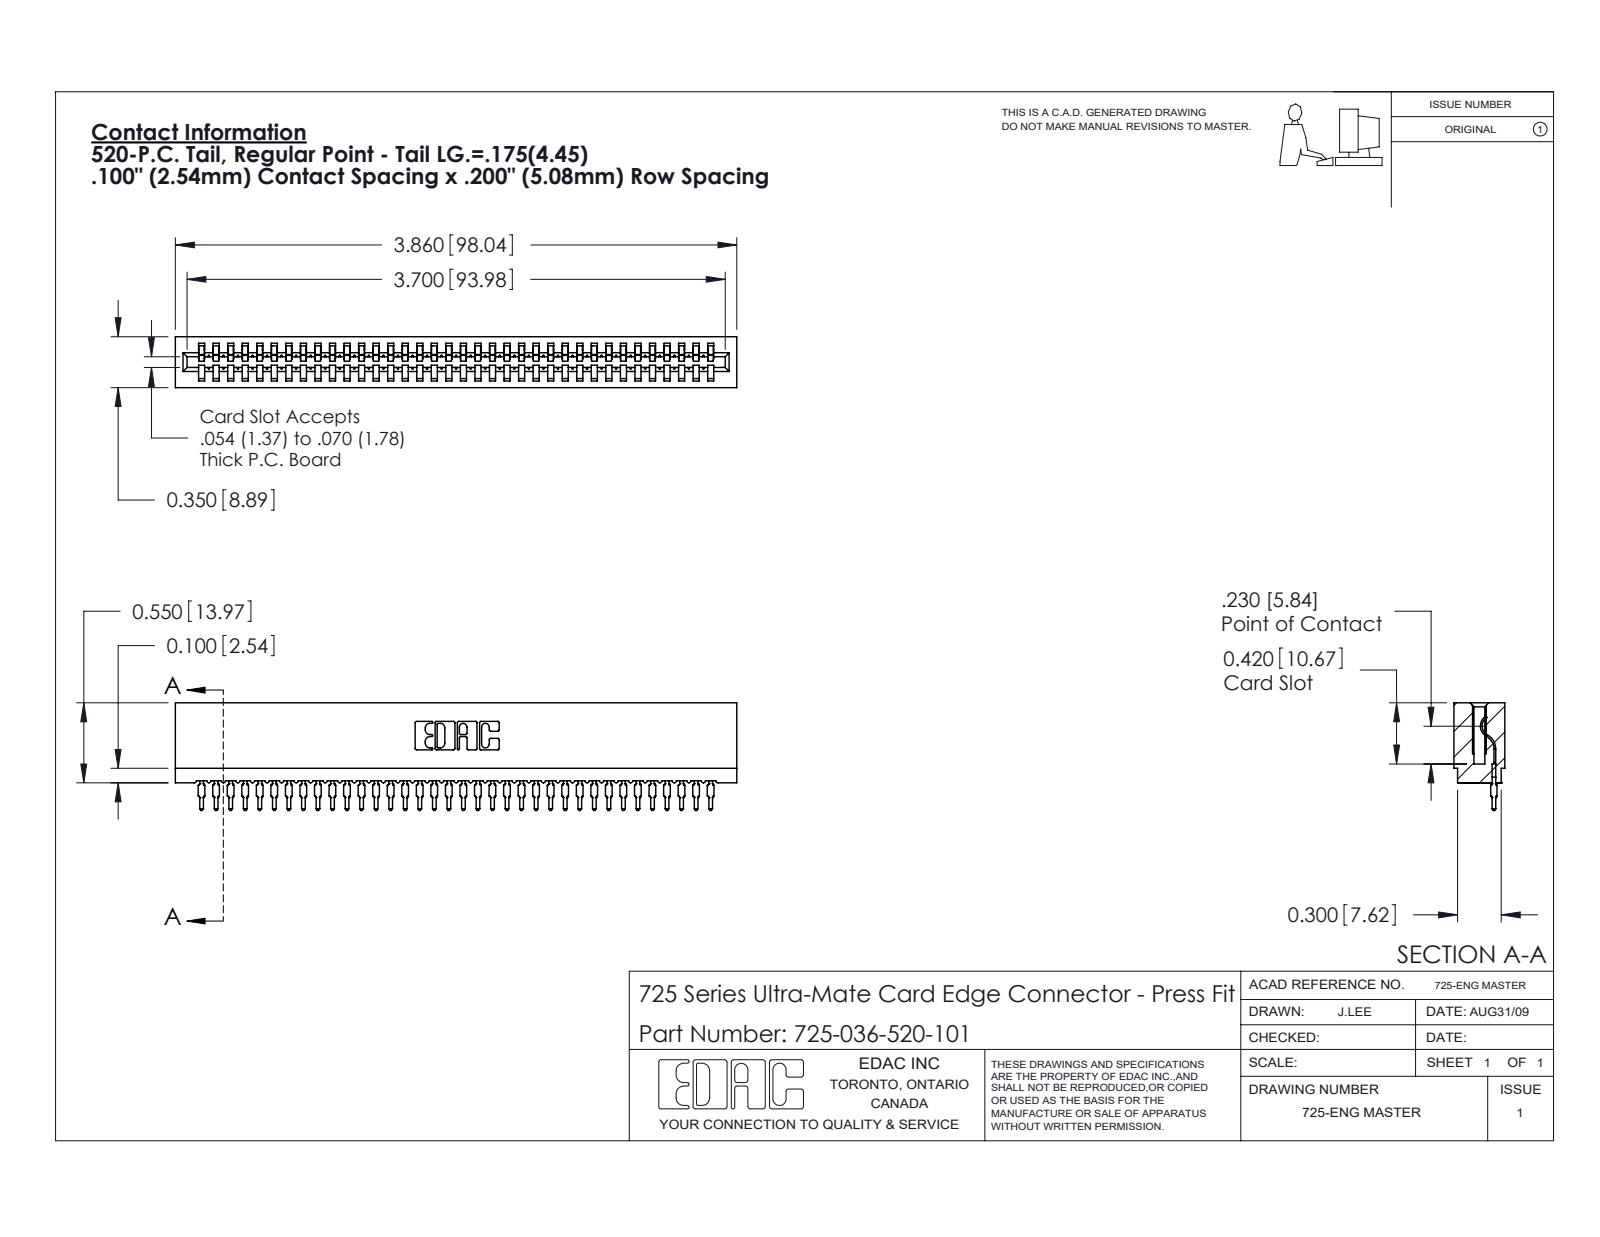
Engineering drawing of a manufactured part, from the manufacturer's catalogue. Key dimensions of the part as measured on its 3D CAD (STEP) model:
Part name (STEP PRODUCT): 725 Part_Insulator Option - 01; 725-036-520-101; 745-292-001_520
STEP written by: SolidWorks 2020 (CONFIG_CONTROL_DESIGN)
Units: inches
Bodies: 37 solids, 4127 faces (2467 planar, 724 cylindrical, 936 other)
Overall size (bounding box): 3.86 × 0.741 × 0.35
Volume: 0.453 in³ · Surface area: 21.66 in²
Partial cylindrical surfaces — rounded edges, fillets, slot ends (radius × count): R0.015 ×72, R0.021 ×72, R0.01 ×22, R0.007 ×6, R0.031 ×6, R0.005 ×4, R0.011 ×4, R0.026 ×3
Main face-to-face distances: 0.35, 0.212, 0.138, 0.2, 0.1, 0.045, 0.305, 0.093, 0.167, 0.6
